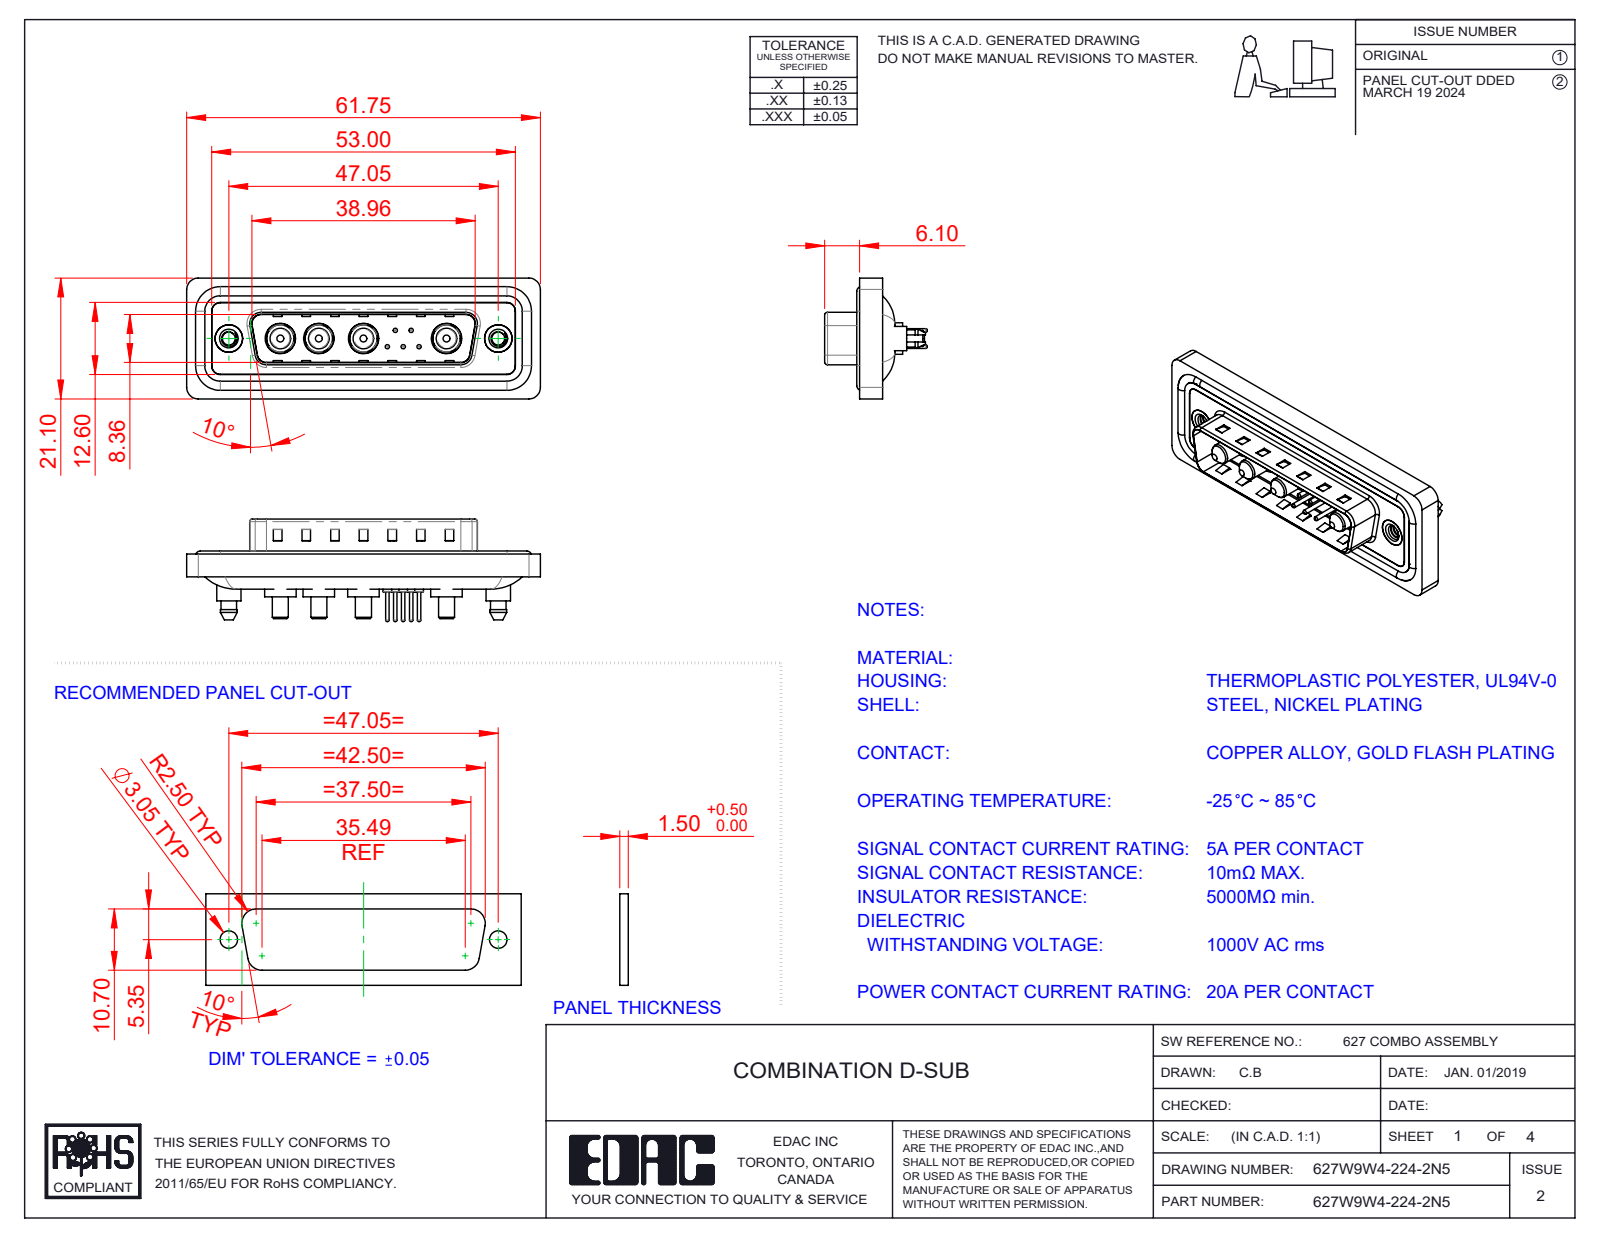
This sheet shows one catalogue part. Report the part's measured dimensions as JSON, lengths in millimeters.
{"part_name": "627Combo Shell Front_25 Contacts; 627Combo Waterproof Housing_25 Contacts; 627Combo Contact Row 2_24; 627W9W4-224-2N5 (+5 more)", "step_written_by": "SolidWorks 2023 (CONFIG_CONTROL_DESIGN)", "units": "millimeters", "bodies": {"solids": 20, "faces": 874, "planar": 300, "cylindrical": 366, "other": 208}, "overall_size": [61.75, 21.1, 17.9], "volume_mm3": 7538, "surface_area_mm2": 12168, "round_holes": [[0.75, 5], [1.6, 5], [2, 5], [4.85, 4], [5.3, 4], [2.26, 2], [4, 2], [4.8, 2], [5, 2]], "round_bosses_or_shafts": [[1.5, 5], [0.6, 5], [5.5, 4], [5.2, 4], [4.75, 4], [3.75, 4], [3.6, 4], [2.8, 4]], "partial_cylinders_radius": [[1.5, 24], [2, 18], [1.6, 10], [0.5, 8], [0.25, 4], [0.6, 4], [0.65, 4], [0.9, 4]], "face_to_face_distances": [0.4, 1.5, 1.1, 0.5, 3.1, 1.6, 2.9, 0.82, 9.58, 5.65], "hole_center_spacings": [3.16, 2.77, 5.04, 14.51, 2.78, 4.4, 4.41, 5]}
